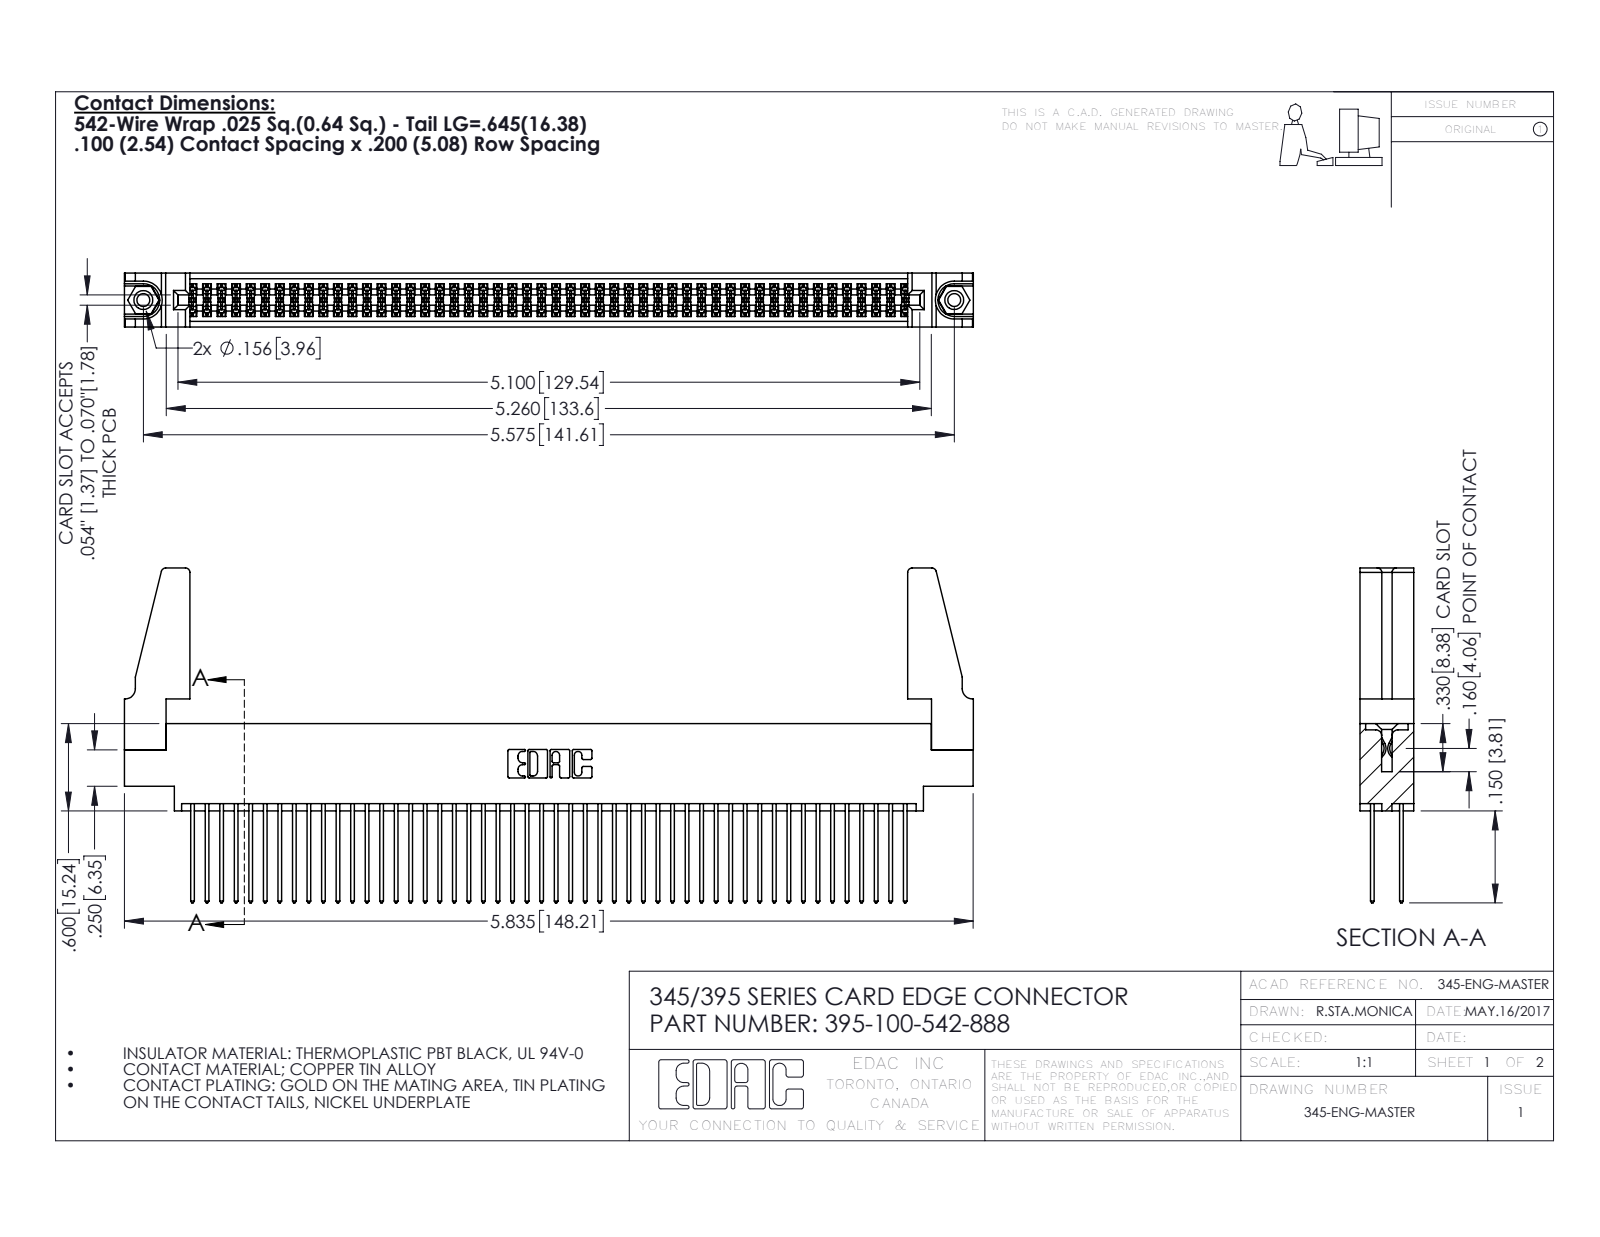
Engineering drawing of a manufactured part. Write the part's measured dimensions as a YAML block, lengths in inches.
part_name: "345 Part_0.170 Offset - 0.156 Dia-TH; 345-250-001_345-250-001-102; 345-292-001_345-293-142; 395-100-542-888 (+1 more)"
step_written_by: "SolidWorks 2016 (CONFIG_CONTROL_DESIGN)"
units: inches
bodies: {solids: 105, faces: 5254, planar: 3456, cylindrical: 1782, other: 16}
overall_size: [5.836, 2.302, 0.37]
volume: 1.103
surface_area: 42.65
round_holes:
  - {diameter: 0.089, count: 2}
  - {diameter: 0.125, count: 2}
  - {diameter: 0.156, count: 2}
  - {diameter: 0.064, count: 1}
round_bosses_or_shafts:
  - {diameter: 0.155, count: 2}
partial_cylinders:
  - {radius: 0.006, count: 150}
  - {radius: 0.01, count: 100}
  - {radius: 0.01, count: 22}
  - {radius: 0.03, count: 8}
  - {radius: 0.007, count: 6}
  - {radius: 0.031, count: 6}
  - {radius: 0.026, count: 3}
  - {radius: 0.014, count: 2}
face_to_face_distances: [0.072, 0.298, 0.098, 0.272, 0.025, 0.2, 0.37, 0.225, 0.175, 0.149]
hole_center_spacings: [0.27, 5.339, 5.575]
